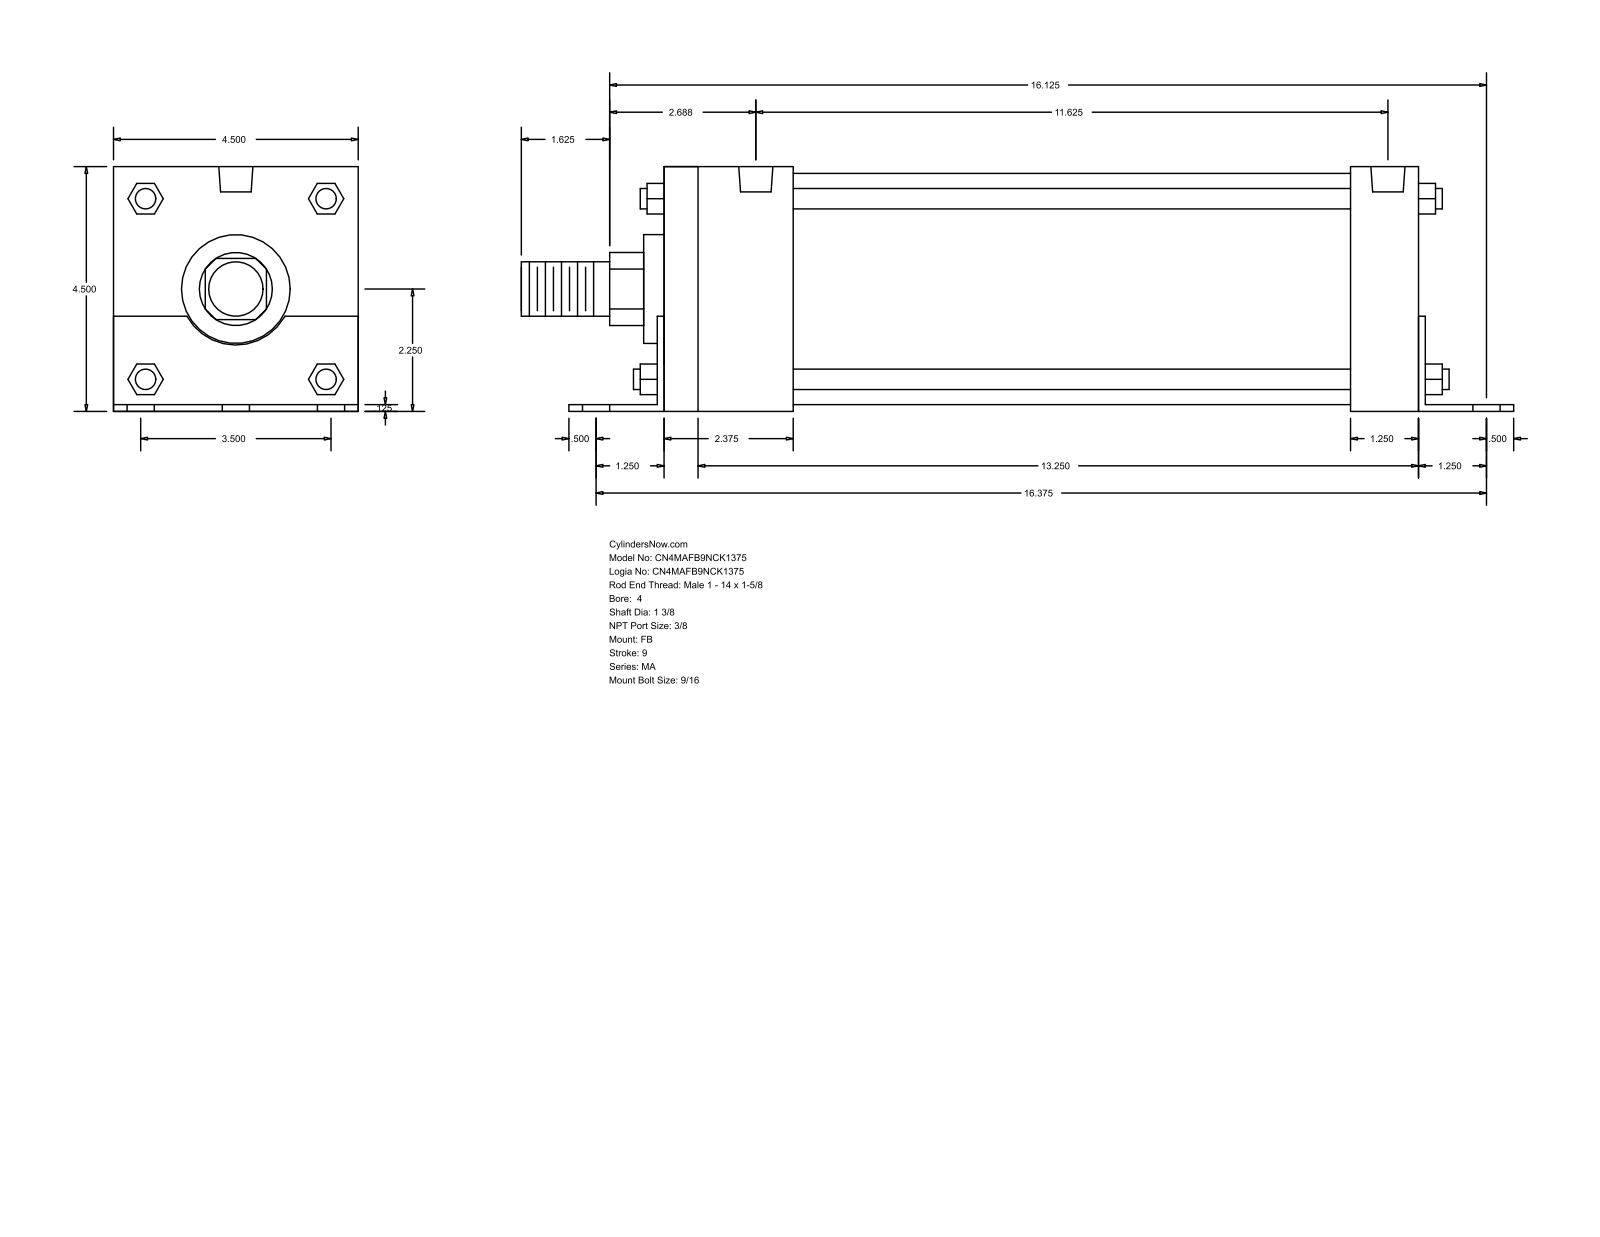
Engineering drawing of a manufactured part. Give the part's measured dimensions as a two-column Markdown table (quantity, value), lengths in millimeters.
| quantity | value |
| --- | --- |
| part name | MA_FB__0400_1.375 |
| STEP written by | GSSL Pune (CONFIG_CONTROL_DESIGN) |
| units | millimeters |
| bodies | 0 solids, 140 faces (105 planar, 35 cylindrical, 0 other) |
| overall size | 463.55 × 114.35 × 114.3 |
| round holes (diameter × count) | 14.29 × 6, 11.11 × 4, 15.93 × 2 |
| round bosses / shafts (diameter × count) | 9.53 × 4, 107.95 × 1, 50.8 × 1, 34.92 × 1, 25.4 × 1 |
| partial cylindrical surfaces (radius × count) | 17.06 × 1, 26.16 × 1 |
| main face-to-face distances | 114.3, 3.17, 114.35, 3.12, 111.18, 352.42, 3.18, 355.6, 34.93, 355.59 |
| hole center spacings | 44.45, 418.29, 415.92, 4.77, 63.99, 67.5, 86.85, 88.9 |
